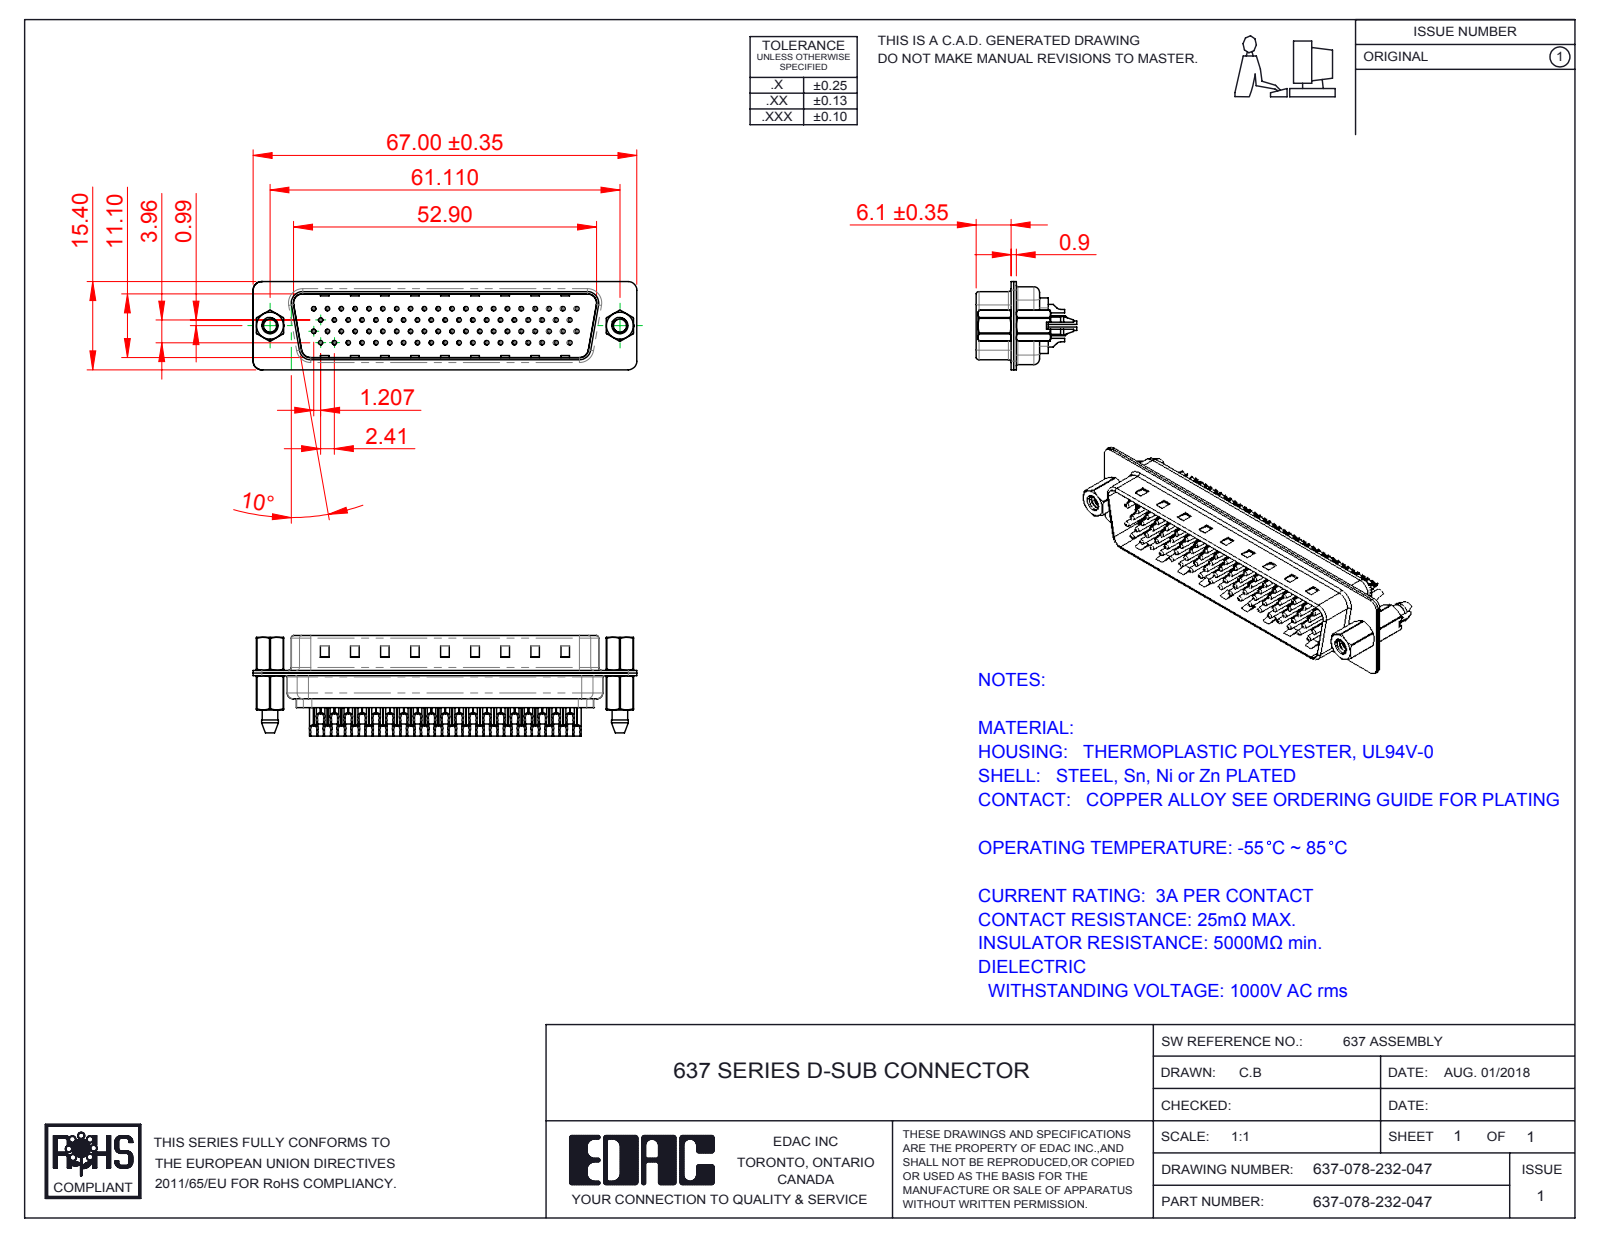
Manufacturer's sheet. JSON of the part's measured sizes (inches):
{"part_name": "637 Shell Rear_78 Contacts; 637 4-40 Threaded Boardlock_LP; 637 Contact Row 1_32(78); 637 Contact Row 2_32(78) (+6 more)", "step_written_by": "SolidWorks 2016 (CONFIG_CONTROL_DESIGN)", "units": "inches", "bodies": {"solids": 85, "faces": 5604, "planar": 1349, "cylindrical": 2507, "other": 1748}, "overall_size": [2.638, 0.691, 0.606], "volume_in3": 0.29, "surface_area_in2": 27.2, "round_holes": [[0.063, 150], [0.014, 78], [0.043, 78], [0.03, 72], [0.079, 72], [0.157, 3], [0.089, 2], [0.09, 2], [0.189, 2]], "round_bosses_or_shafts": [[0.079, 78], [0.059, 78], [0.03, 78], [0.193, 2], [0.11, 2], [0.189, 1]], "partial_cylinders_radius": [[0.059, 18], [0.079, 12], [0.02, 8], [0.039, 8], [0.063, 6], [0.01, 4], [0.022, 4], [0.028, 4]], "face_to_face_distances": [0.018, 0.016, 0.077, 0.059, 0.469, 0.453, 0.028, 0.437, 0.035, 0.031], "hole_center_spacings": [0.095, 0.285, 0.239, 0.38, 0.274, 0.333, 0.572, 0.665]}
